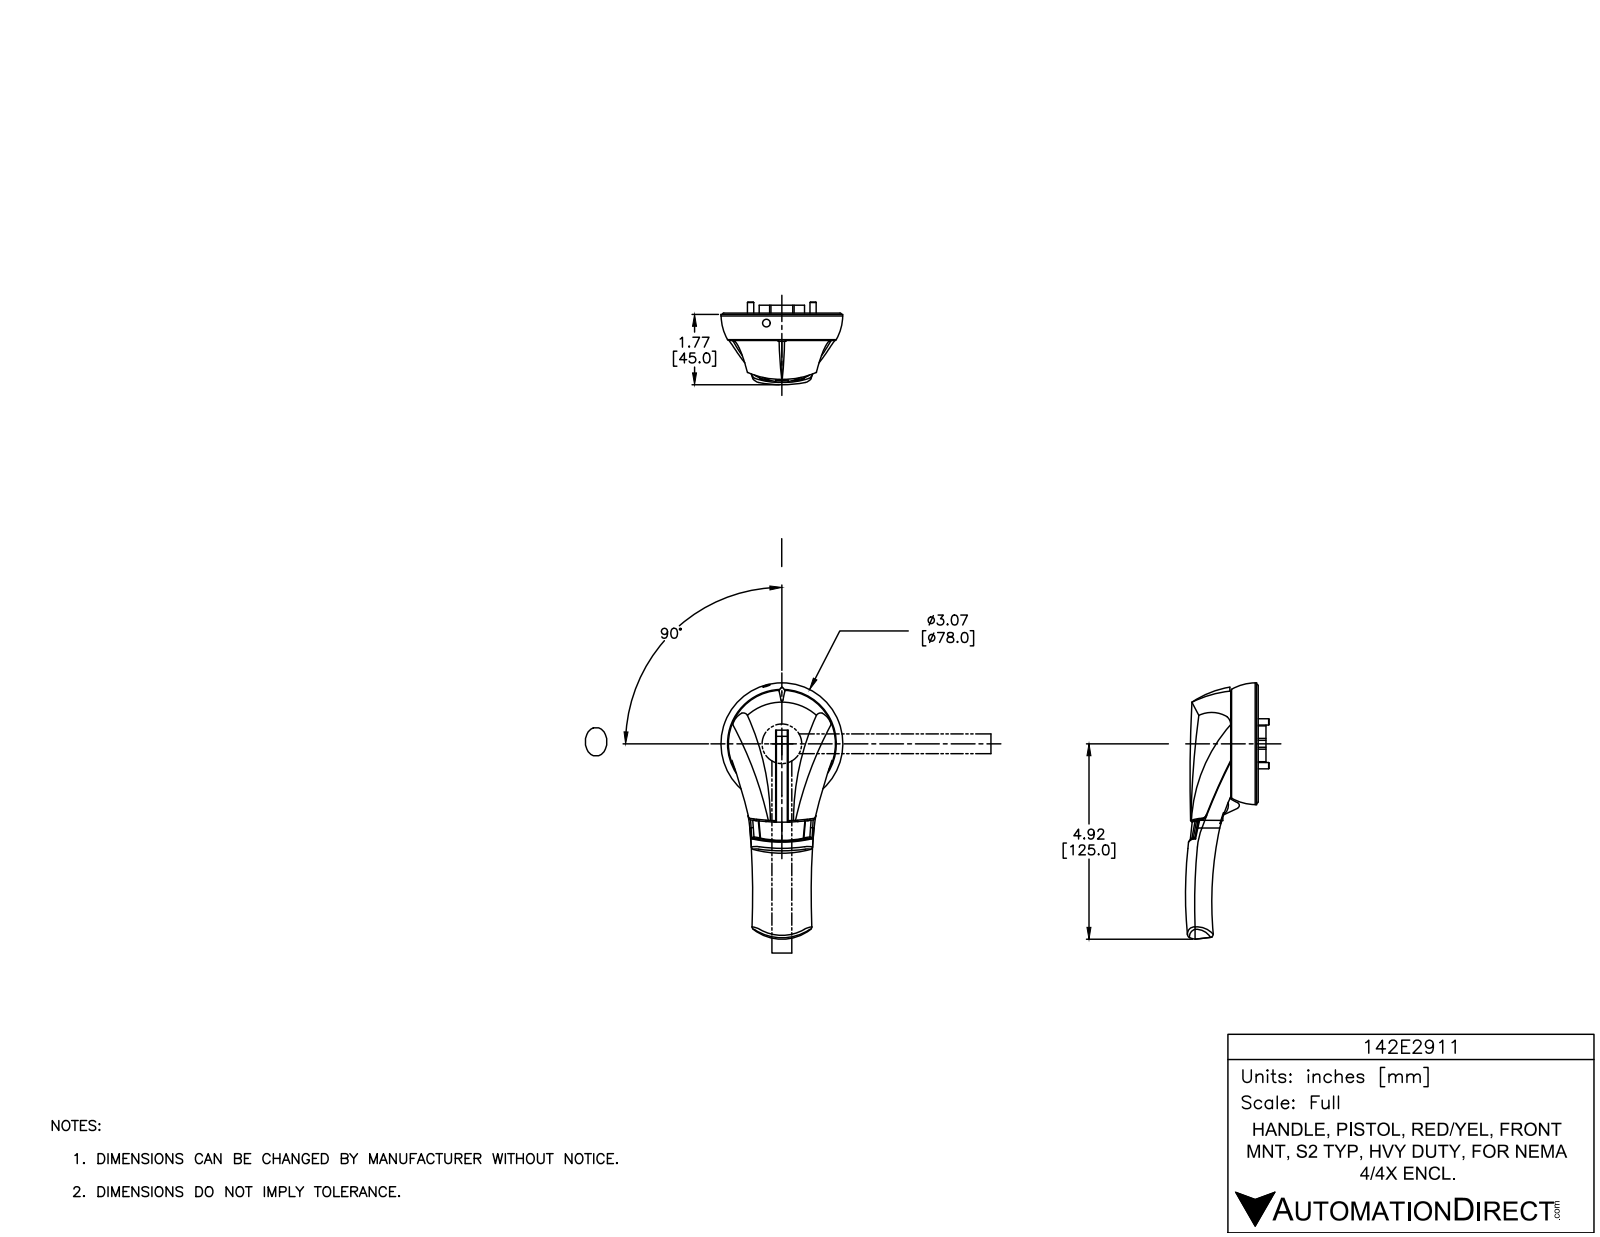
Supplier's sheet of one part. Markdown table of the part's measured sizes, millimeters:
| quantity | value |
| --- | --- |
| part name | 142E2911 |
| STEP written by | SolidWorks 2015 (AUTOMOTIVE_DESIGN) |
| units | millimeters |
| bodies | 8 solids, 1516 faces (810 planar, 548 cylindrical, 158 other) |
| overall size | 164 × 78 × 52.8 |
| volume | 155 900 mm³ |
| surface area | 56 340 mm² |
| round holes (diameter × count) | 4 × 6, 8.6 × 4, 10.8 × 4, 0.8 × 3, 4.3 × 2, 9.2 × 2, 3 × 1, 4.8 × 1, 76 × 1 |
| round bosses / shafts (diameter × count) | 0.5 × 11, 8.5 × 4, 8 × 4, 2.3 × 3, 1.8 × 3, 5.8 × 2, 71.6 × 1, 68.6 × 1 |
| partial cylindrical surfaces (radius × count) | 0.3 × 221, 0.4 × 20, 0.9 × 20, 0.8 × 15, 1 × 4, 0.6 × 3, 138.1 × 3, 2 × 2 |
| main face-to-face distances | 0.6, 17.8, 18.1, 17.5, 0.9, 2.6, 7, 4.4, 6.2, 1.2 |
| hole center spacings | 24.4, 7.8, 17, 27.9, 28, 30.6, 40, 47.8 |
